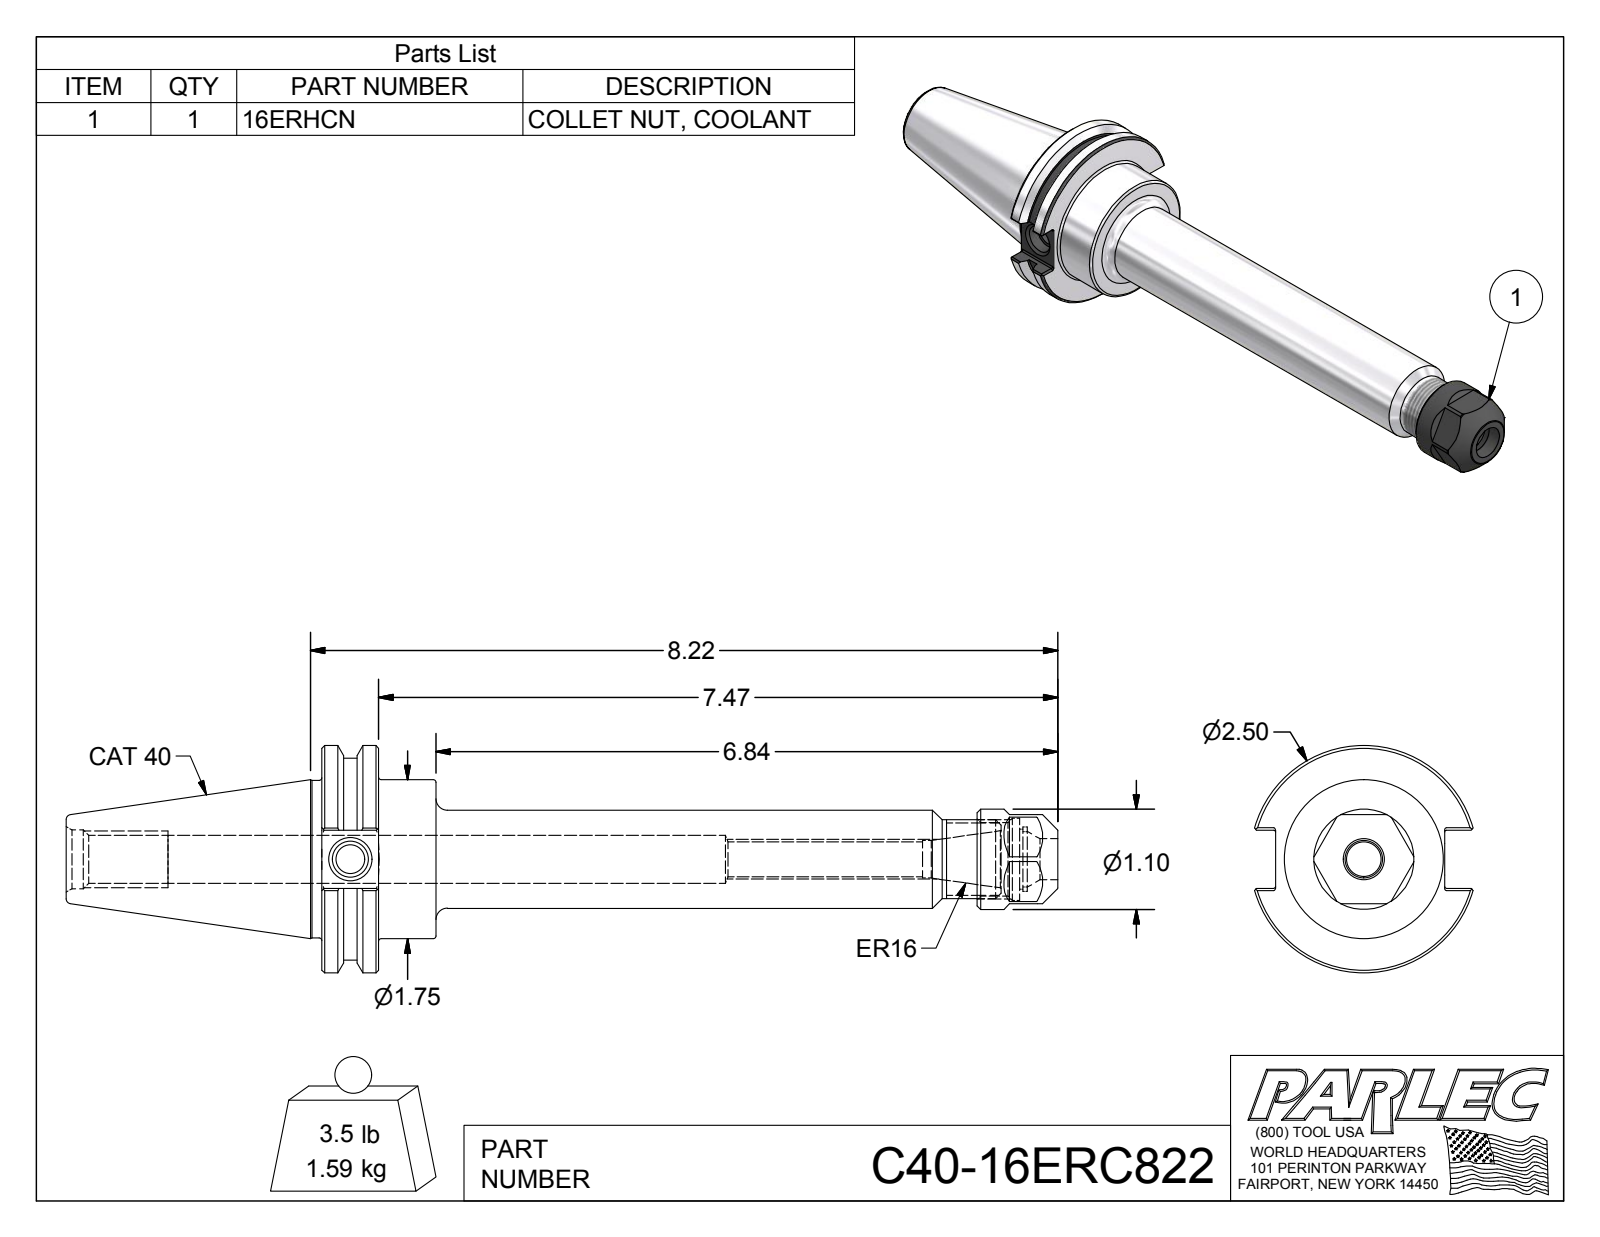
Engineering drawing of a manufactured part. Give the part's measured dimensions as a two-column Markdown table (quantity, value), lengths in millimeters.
| quantity | value |
| --- | --- |
| part name | C40-16ER8-1; 16ERHCN; C40-16ERC822 |
| STEP written by | Autodesk Inventor 2016 (AUTOMOTIVE_DESIGN) |
| units | millimeters |
| bodies | 2 solids, 122 faces (50 planar, 35 cylindrical, 37 other) |
| overall size | 277.05 × 63.5 × 61.05 |
| volume | 200 256 mm³ |
| surface area | 45 905 mm² |
| round holes (diameter × count) | 8 × 1, 9.73 × 1, 10.13 × 1, 10.5 × 1, 11.5 × 1, 13.38 × 1, 13.39 × 1, 16.46 × 1, 16.8 × 1, 20.5 × 1, 23 × 1 |
| round bosses / shafts (diameter × count) | 63.5 × 1, 56.36 × 1, 44.45 × 1, 43.94 × 1, 28 × 1, 27.43 × 1, 22 × 1 |
| partial cylindrical surfaces (radius × count) | 0.51 × 12, 9 × 1 |
| main face-to-face distances | 15.88, 31.88, 16, 24.86, 4.3, 20.56, 194.92, 179.04, 163.04, 16.26 |
| hole center spacings | 1.3 |
